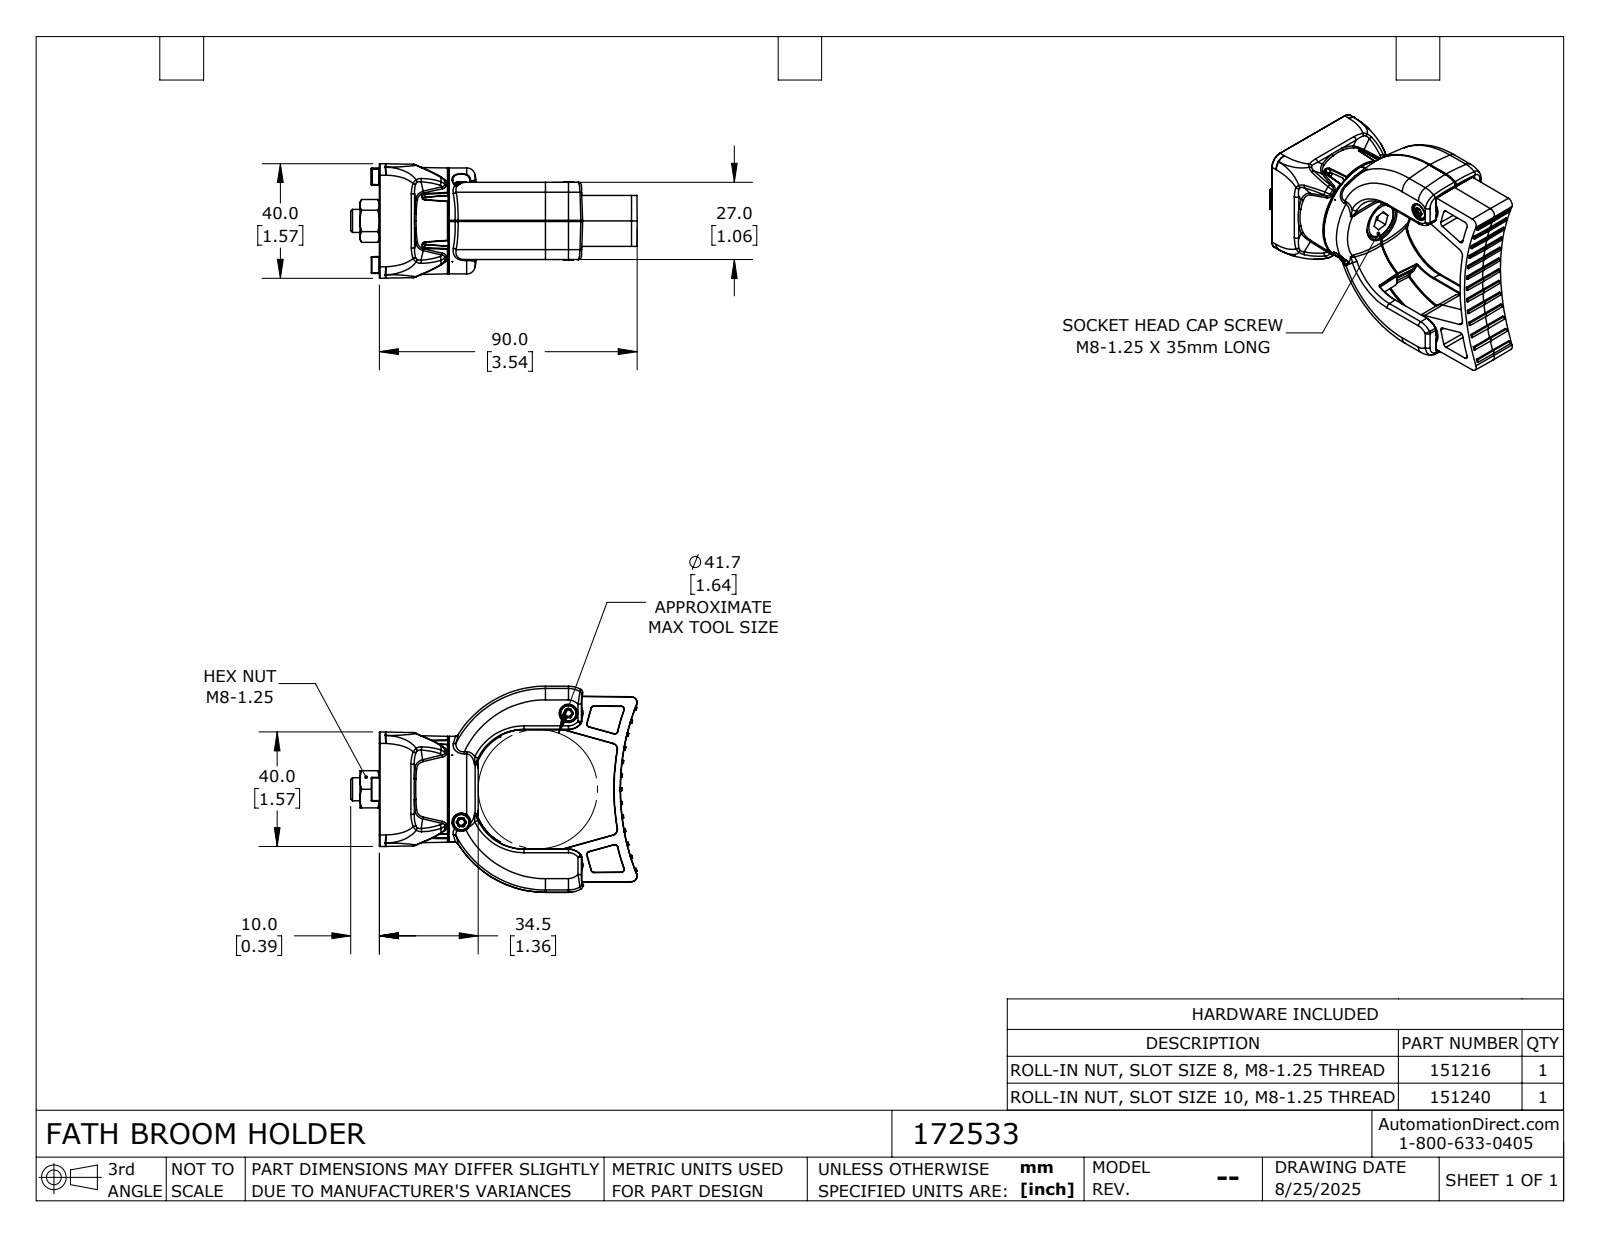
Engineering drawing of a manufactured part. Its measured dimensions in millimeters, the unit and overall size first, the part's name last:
Units: millimetres
Overall size (bounding box): 100 × 71.99 × 40
Round holes (diameter × count): ⌀3.4 ×4, ⌀2.5 ×2, ⌀2.6 ×2, ⌀4.16 ×2, ⌀5.1 ×2, ⌀6.8 ×1, ⌀8 ×1, ⌀9 ×1, ⌀13.01 ×1, ⌀14 ×1
Round bosses / shafts (diameter × count): ⌀5.6 ×4, ⌀9.5 ×2, ⌀7.1 ×2, ⌀4.14 ×2, ⌀2.6 ×2, ⌀37 ×1, ⌀31 ×1, ⌀13 ×1
Partial cylindrical surfaces — rounded edges, fillets, slot ends (radius × count): R0.2 ×184, R0.5 ×14, R0.3 ×12, R1.2 ×12, R4 ×12, R1 ×8, R106.26 ×4, R16.5 ×1
Main face-to-face distances: 13.5, 4.2, 22.8, 9.3, 18.2, 4.6, 22.4, 0.4, 8.9, 3.4
Hole centre spacings: 14.43, 27.46, 34.6, 40.3, 53.32, 55.07, 23, 43
Volume: 66 056 mm³ · Surface area: 40 287 mm²
Bodies: 15 solids, 2197 faces (512 planar, 469 cylindrical, 1216 other)
Part name (STEP PRODUCT): 172533
STEP written by: SolidWorks 2024 (CONFIG_CONTROL_DESIGN)
